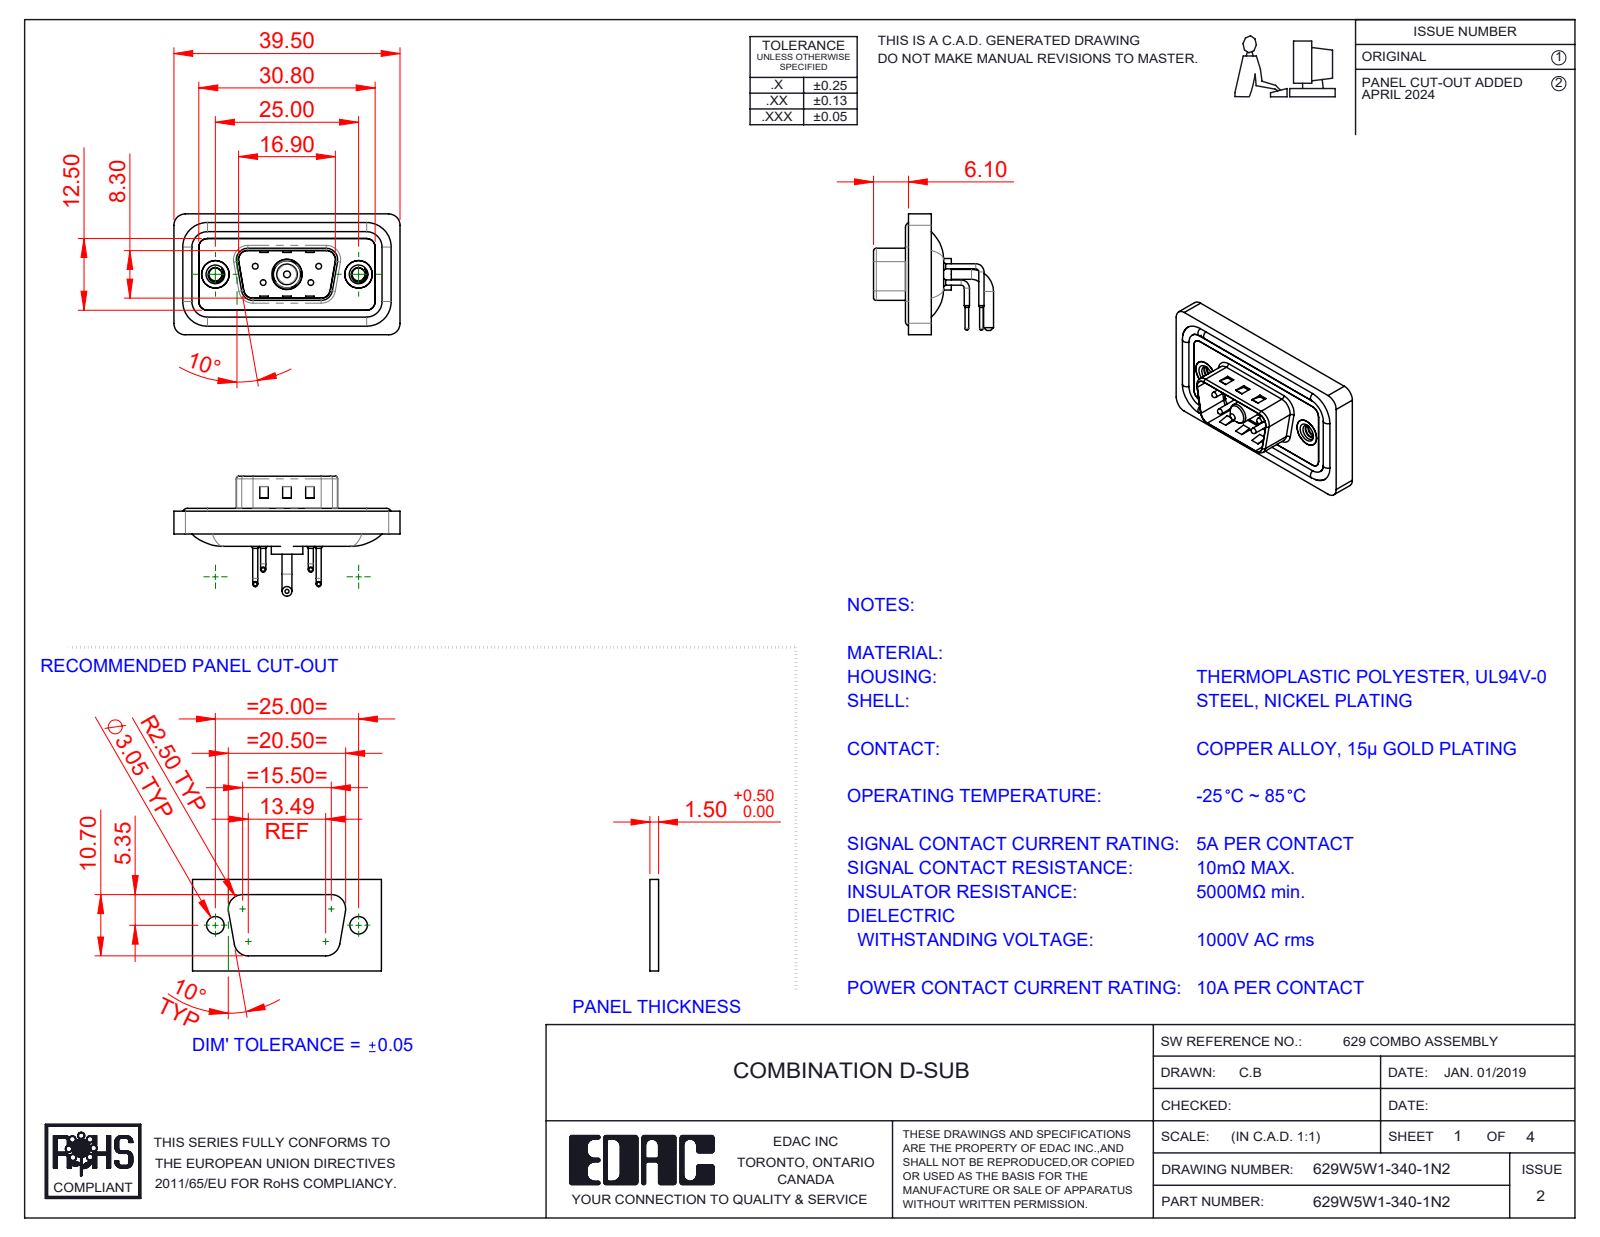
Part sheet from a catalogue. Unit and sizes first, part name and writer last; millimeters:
Units: millimetres
Overall size (bounding box): 39.5 × 21.1 × 20.95
Round holes (diameter × count): ⌀0.75 ×4, ⌀1.6 ×4, ⌀2 ×4, ⌀2.26 ×2, ⌀4 ×2, ⌀4.8 ×2, ⌀5 ×2, ⌀4.85 ×1, ⌀5.3 ×1
Round bosses / shafts (diameter × count): ⌀0.9 ×8, ⌀1.6 ×4, ⌀1.5 ×4, ⌀1 ×4, ⌀0.65 ×4, ⌀4.9 ×2, ⌀1.7 ×2, ⌀5.5 ×1
Partial cylindrical surfaces — rounded edges, fillets, slot ends (radius × count): R1.5 ×18, R2 ×18, R0.5 ×8, R1.6 ×8, R0.25 ×4, R0.6 ×4, R0.65 ×4, R0.9 ×4
Main face-to-face distances: 0.4, 2.9, 1.1, 0.8, 2.1, 2.5, 1.6, 3.1, 1.5, 4.5
Hole centre spacings: 3.16, 5.72, 7.1, 12.5, 18.1, 4.39, 4.4, 8.31
Volume: 4 429 mm³ · Surface area: 7 113 mm²
Bodies: 13 solids, 894 faces (411 planar, 345 cylindrical, 138 other)
Part name (STEP PRODUCT): 629Combo Threaded Rivet_2; 629Combo Waterproof Housing_09 Contacts; 629Combo Contact Row 2; Power Pin_10A RA (+5 more)
STEP written by: SolidWorks 2023 (CONFIG_CONTROL_DESIGN)
